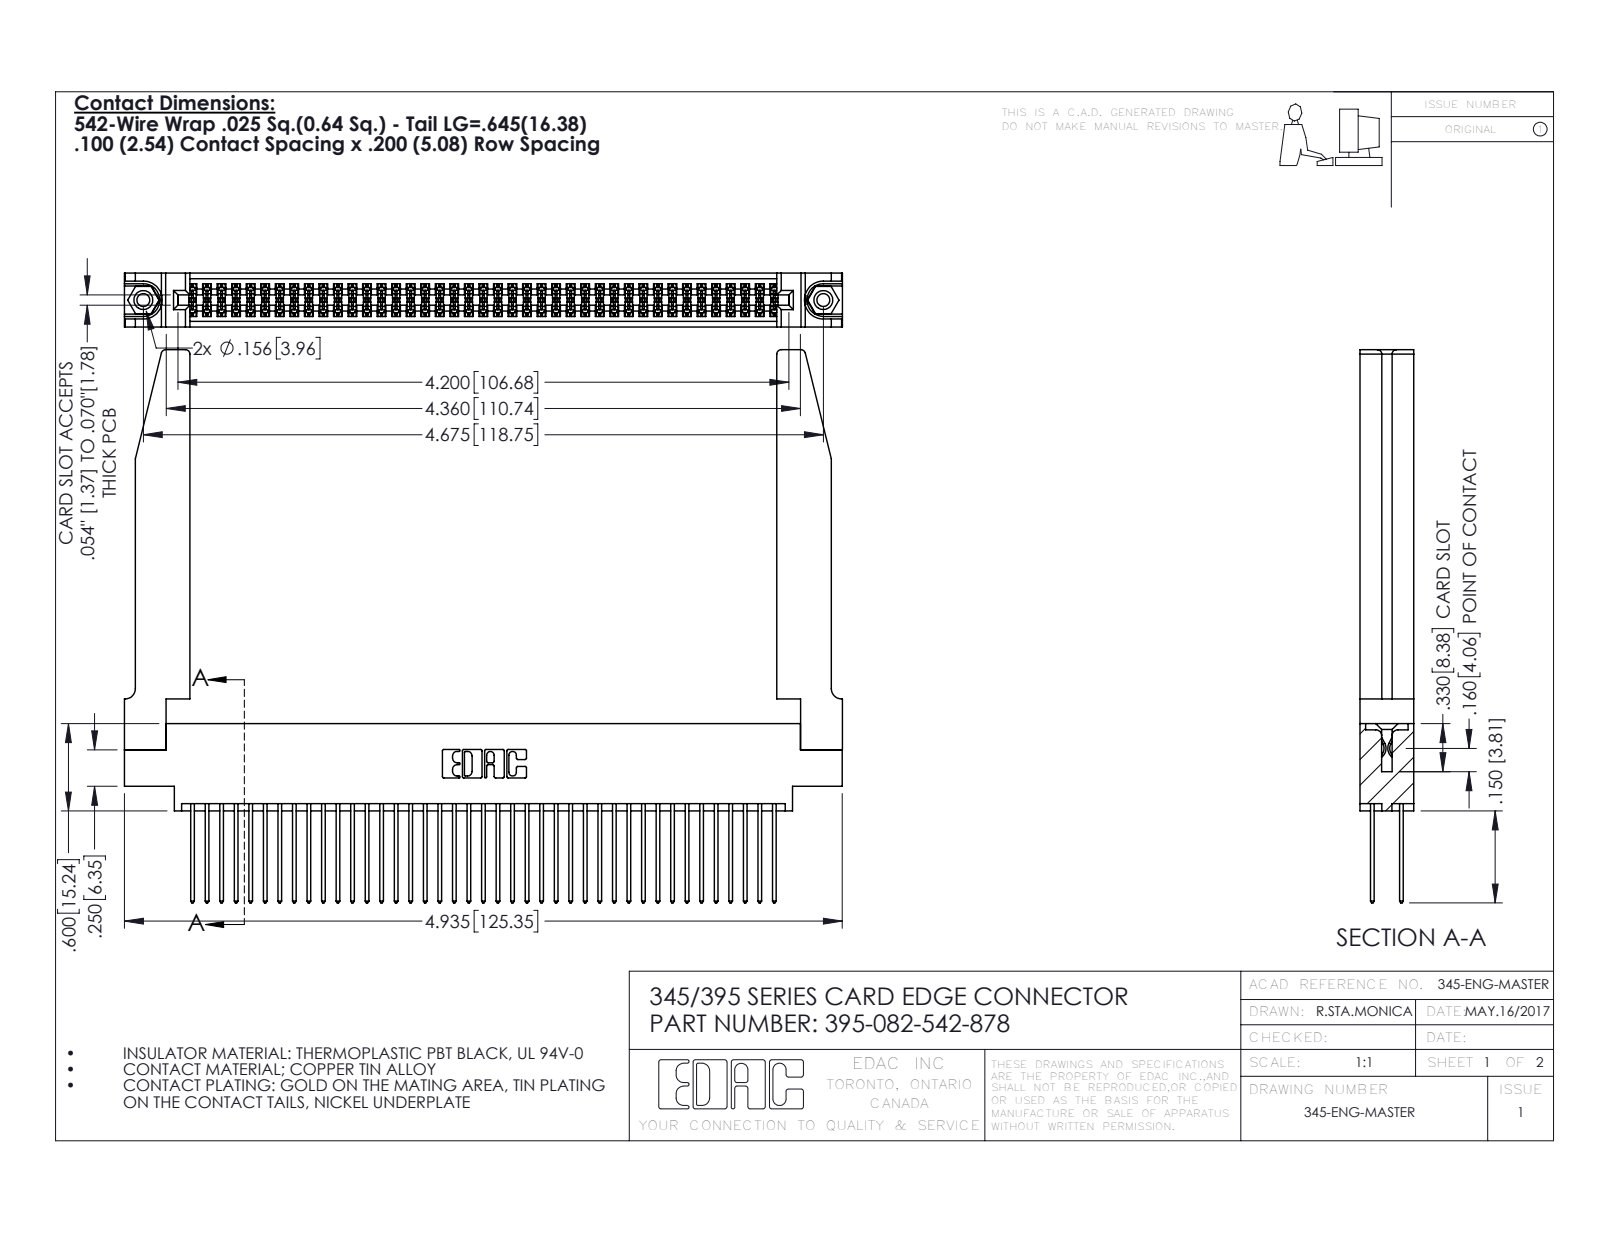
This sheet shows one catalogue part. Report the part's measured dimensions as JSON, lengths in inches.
{"part_name": "345-292-001_345-293-142; 345-220-078_345-220-078; 345 Part_0.170 Offset - 0.156 Dia-TH; 395-082-542-878 (+1 more)", "step_written_by": "SolidWorks 2016 (CONFIG_CONTROL_DESIGN)", "units": "inches", "bodies": {"solids": 87, "faces": 4464, "planar": 2932, "cylindrical": 1480, "other": 52}, "overall_size": [4.936, 3.802, 0.37], "volume_in3": 1.233, "surface_area_in2": 42.06, "round_holes": [[0.089, 2], [0.125, 2], [0.156, 2], [0.064, 1]], "round_bosses_or_shafts": [[0.155, 2]], "partial_cylinders_radius": [[0.006, 123], [0.01, 82], [0.01, 22], [0.03, 8], [0.007, 6], [0.031, 6], [0.026, 3], [0.014, 2]], "face_to_face_distances": [0.072, 0.298, 0.37, 0.2, 0.098, 0.272, 0.025, 0.225, 0.175, 0.148], "hole_center_spacings": [0.27, 4.439, 4.675]}
